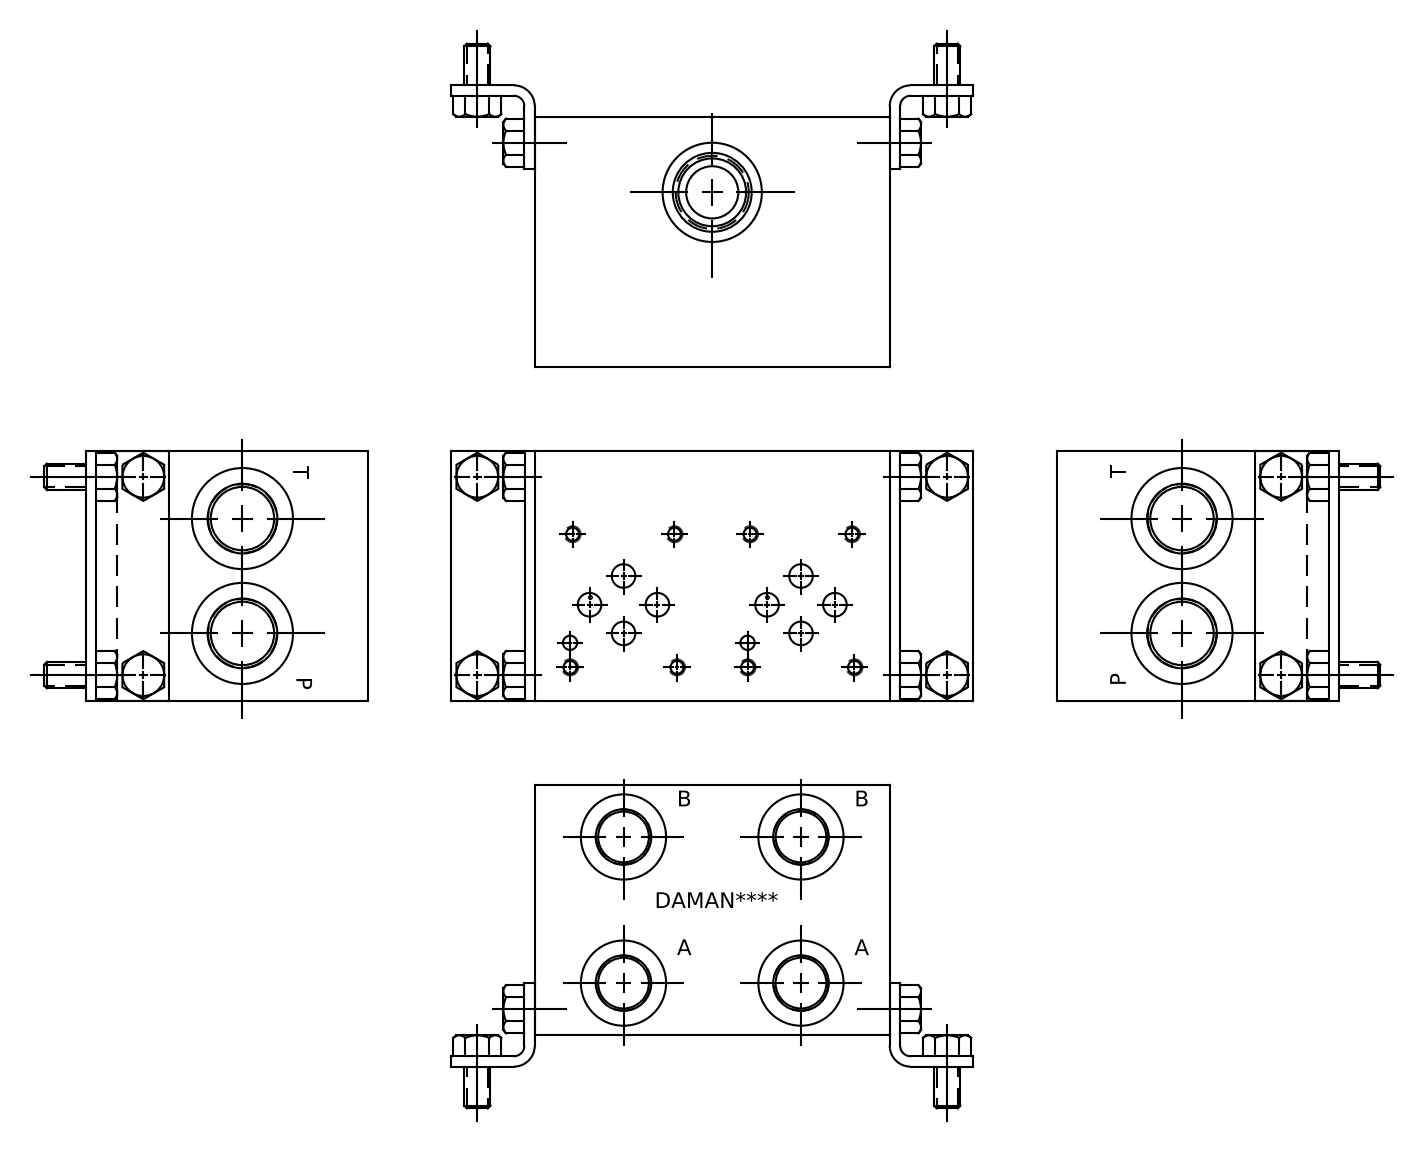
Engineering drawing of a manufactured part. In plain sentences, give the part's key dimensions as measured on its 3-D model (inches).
The part is named "AD03P022B_C". Its 3-D file was written by "Autodesk Inventor 2009 (AUTOMOTIVE_DESIGN)". It is 1 solid with 181 faces: 37 planar, 72 cylindrical and 72 other. Overall it measures 4.25 by 3 by 3 inches. Its volume is 32.79 cubic inches and its surface area 103.6 square inches. Round holes: 8 of diameter 0.166, 8 of diameter 0.197, 6 of diameter 0.281, 4 of diameter 0.593, 4 of diameter 0.656, 4 of diameter 1.021, 3 of diameter 0.562, 2 of diameter 0.172, 2 of diameter 0.25, 2 of diameter 0.266, 2 of diameter 0.315, 2 of diameter 0.438. The main face-to-face distances are 3, 4.25, 0.031, 4.219, 2.969, 4.188, 2.875, 2.844, 0.125, 0.684. The hole center spacings are 2.125, 0.532, 0.868, 1.335, 1.594, 2.026, 2.233, 2.554.
